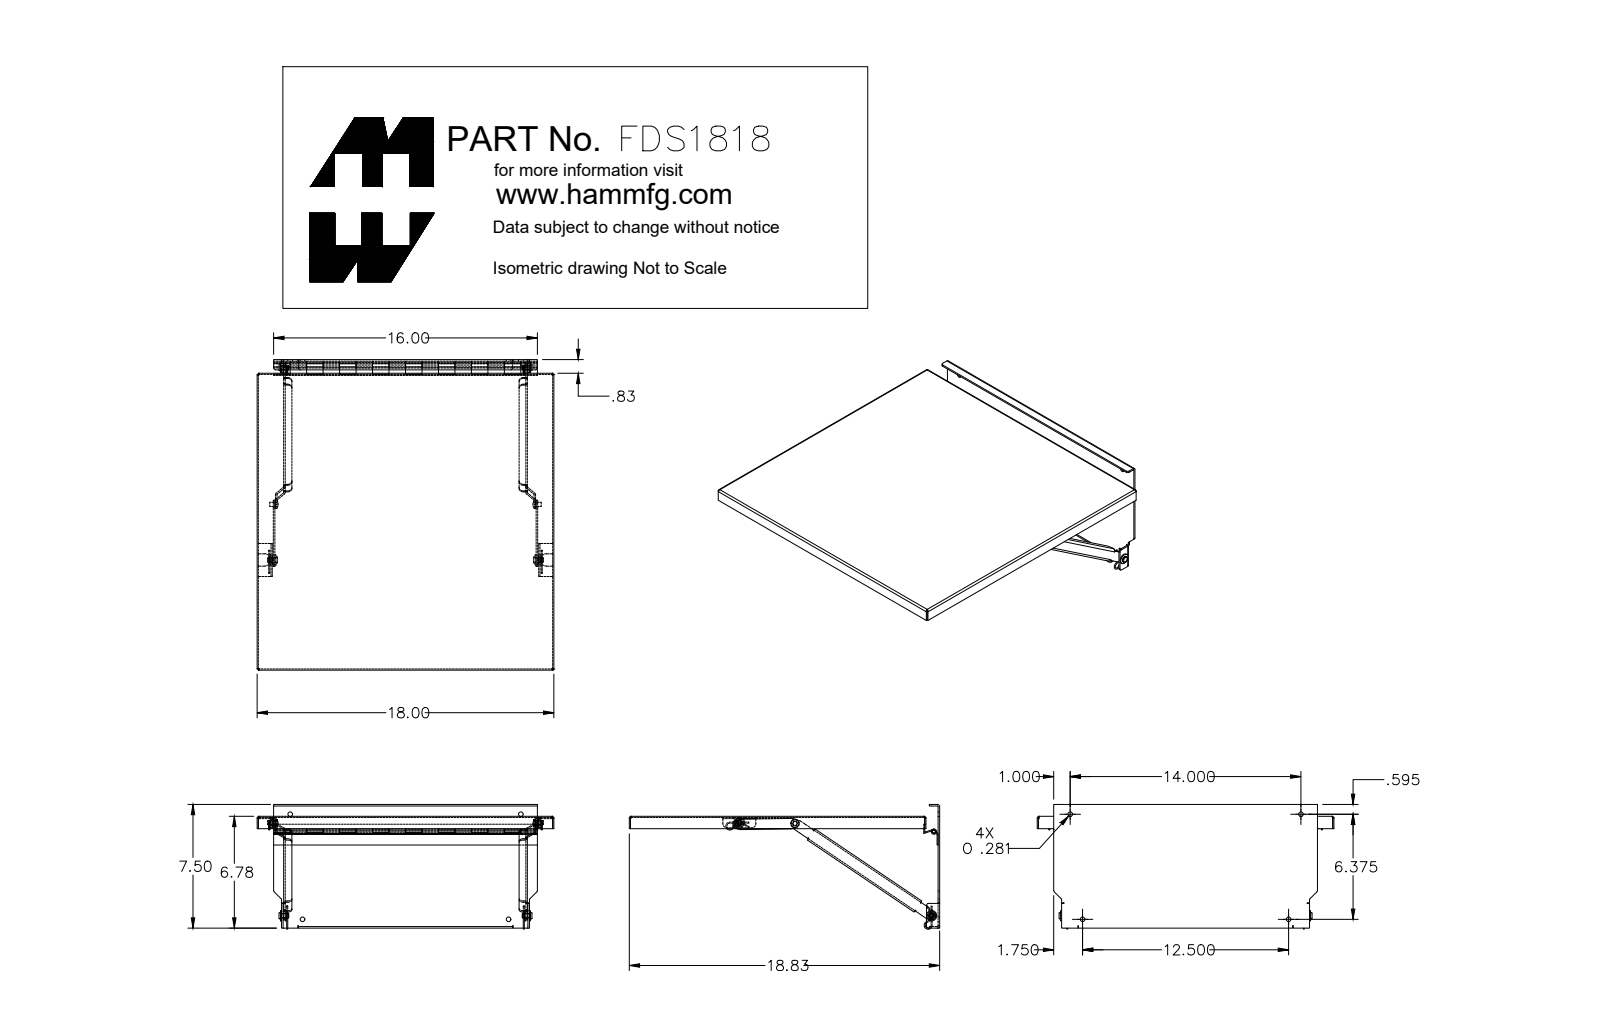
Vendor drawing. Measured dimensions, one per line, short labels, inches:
name: FDS1818GY
written by: SolidWorks 2018 (AUTOMOTIVE_DESIGN)
unit: in
bodies: 15 solids, 386 faces (218 planar, 156 cylindrical, 12 other)
size: 18.831 × 18 × 7.5
volume: 43.94 in³; area: 1 145 in²
holes: 4× ⌀0.281, 2× ⌀0.257, 2× ⌀0.265, 1× ⌀0.187, 1× ⌀0.2, 1× ⌀0.26, 1× ⌀0.265
bosses: 1× ⌀0.51, 1× ⌀0.5, 1× ⌀0.32, 1× ⌀0.25
rounds: 12× R0.25, 10× R0.048, 10× R0.125, 10× R0.143, 6× R0.036, 6× R0.108, 2× R0.375
face distances: 0.072, 0.095, 17.928, 17.856, 18, 0.625, 0.808, 0.903, 18.664, 18.759
hole spacings: 14.704, 0.152, 3.375, 3.517, 5.284, 6.419, 6.419, 8.435
